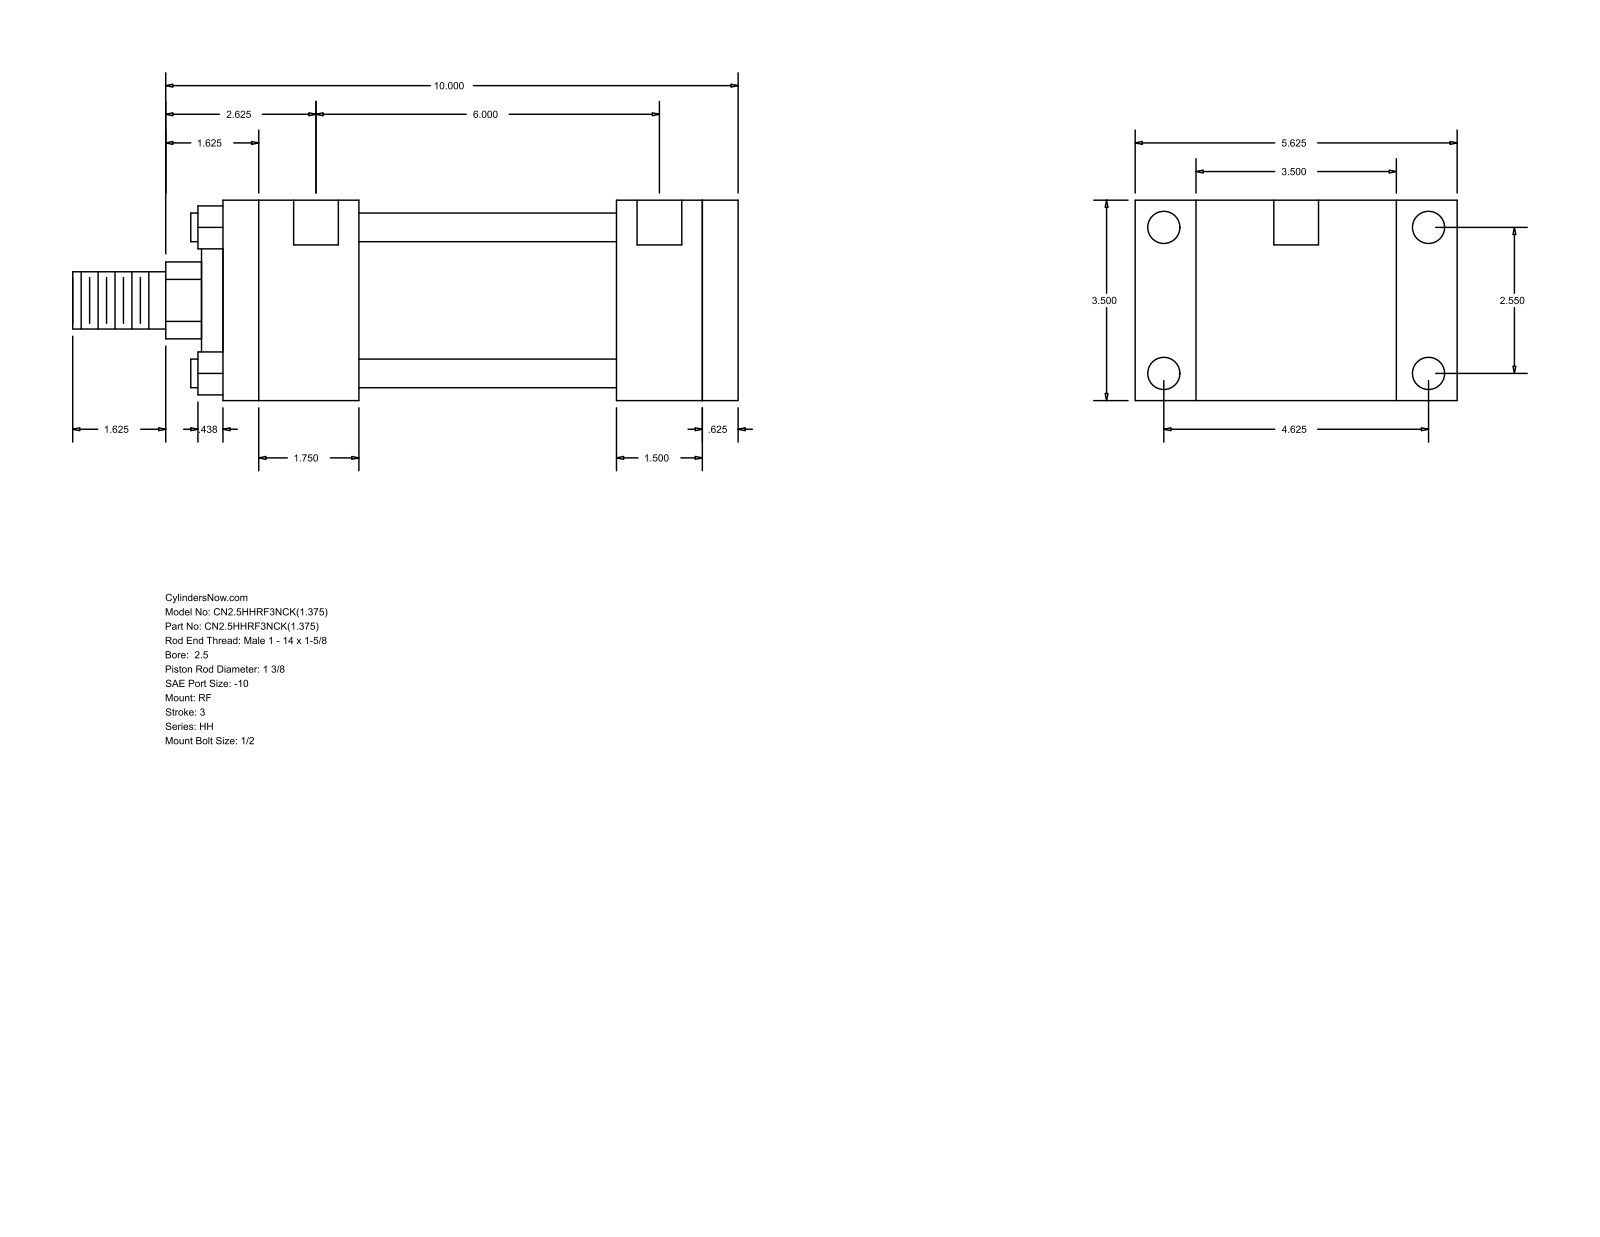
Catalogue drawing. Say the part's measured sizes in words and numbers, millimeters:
The part is named "HH_RF__0250_1.375". Its 3-D file was written by "GSSL Pune (CONFIG_CONTROL_DESIGN)". It is 0 solids with 92 faces: 64 planar, 28 cylindrical and 0 other. Overall it measures 295.27 by 142.88 by 88.9 millimeters. Round holes: 4 of diameter 5.56, 4 of diameter 14.3, 2 of diameter 19.84. Round bosses or shafts: 4 of diameter 12.7, 1 of diameter 73.03, 1 of diameter 50.8, 1 of diameter 34.92, 1 of diameter 25.4. Partial cylindrical surfaces (rounded edges, fillets, slot ends): 1 of radius 17.06. The main face-to-face distances are 88.9, 228.6, 15.88, 212.72, 53.97, 60.32, 152.4, 168.28, 174.63, 114.31. The hole center spacings are 64.76, 117.48, 134.15, 155.57, 1.58, 1.59, 152.4, 153.98.
